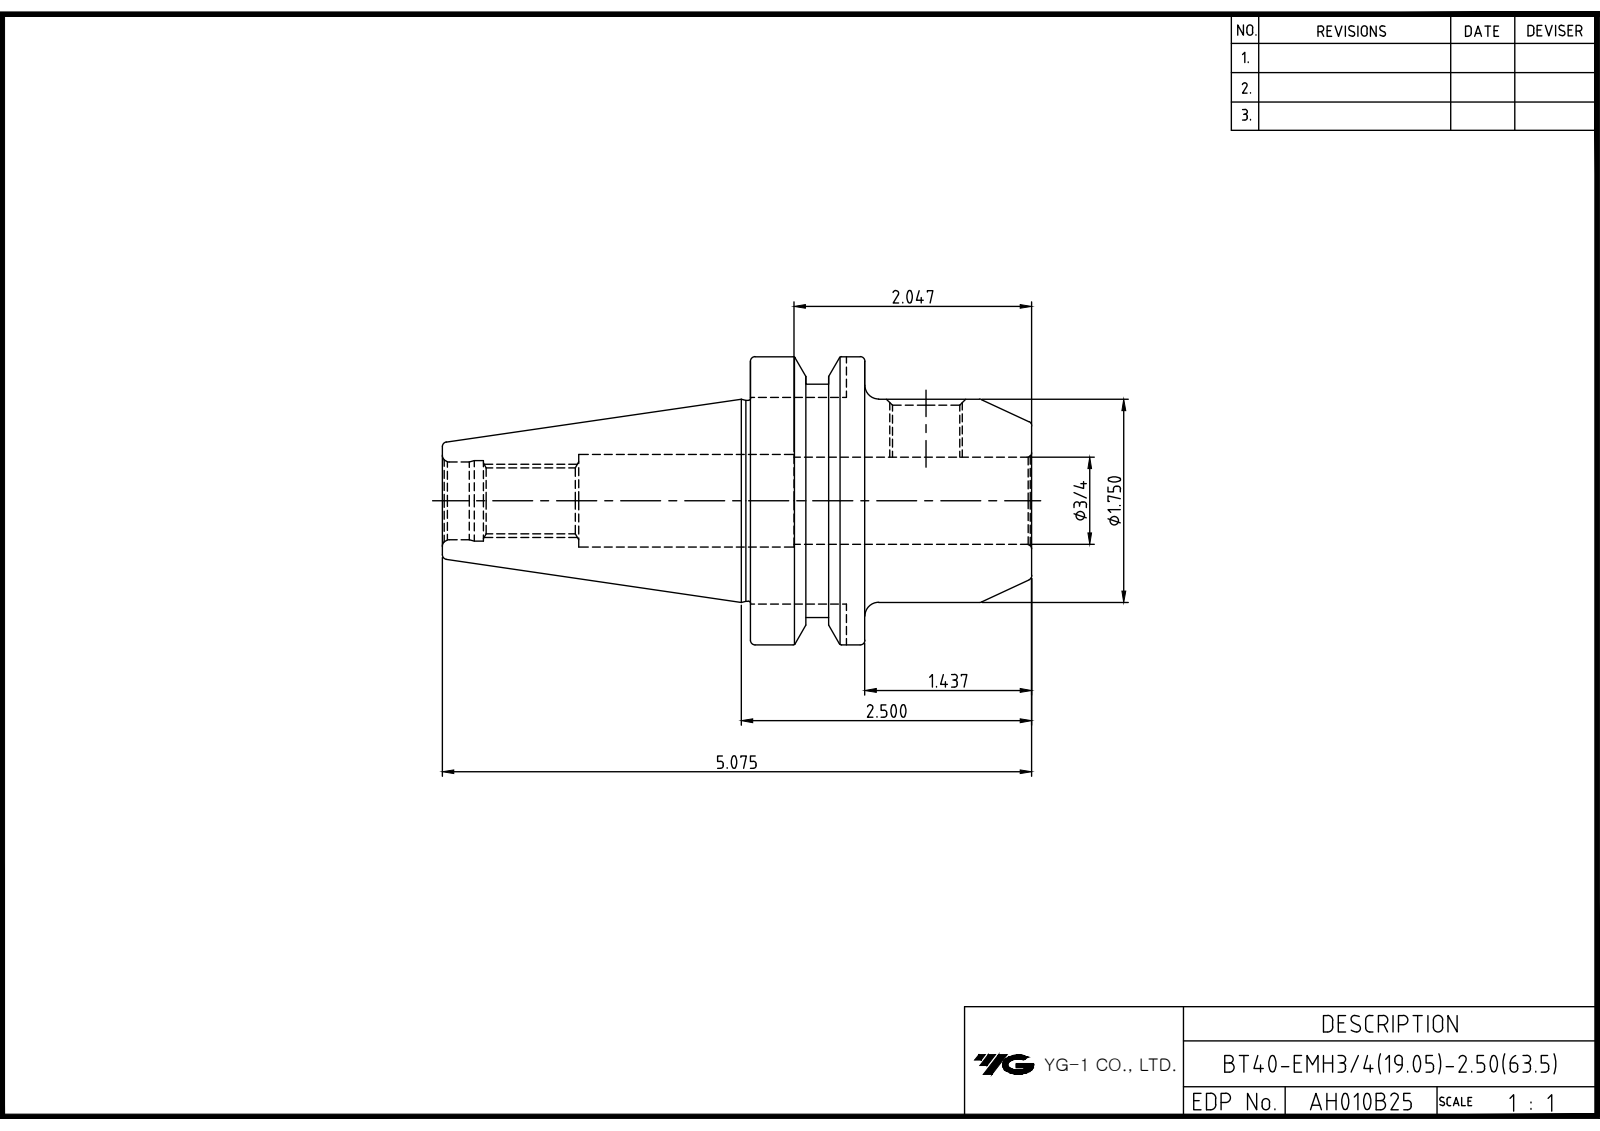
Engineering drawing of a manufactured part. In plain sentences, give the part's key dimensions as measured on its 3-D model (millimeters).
The part is named "LO-BT40-EMH19.05-63.5". Its 3-D file was written by "Autodesk Inventor 2022 (AUTOMOTIVE_DESIGN)". It is 1 solid with 53 faces: 18 planar, 15 cylindrical and 20 other. Overall it measures 128.9 by 63 by 63 millimeters. Its volume is 149 777 cubic millimeters and its surface area 30 333 square millimeters. Round holes: 1 of diameter 13.84, 1 of diameter 14.35, 1 of diameter 17, 1 of diameter 17.6, 1 of diameter 19.05, 1 of diameter 20.25. Round bosses or shafts: 1 of diameter 63, 1 of diameter 52.6, 1 of diameter 44.45, 1 of diameter 44. Partial cylindrical surfaces (rounded edges, fillets, slot ends): 1 of radius 8.05. The main face-to-face distances are 25, 61.5, 36.5, 45.2, 16.1, 67.4, 92.4, 128.9, 84.5, 17.1.
